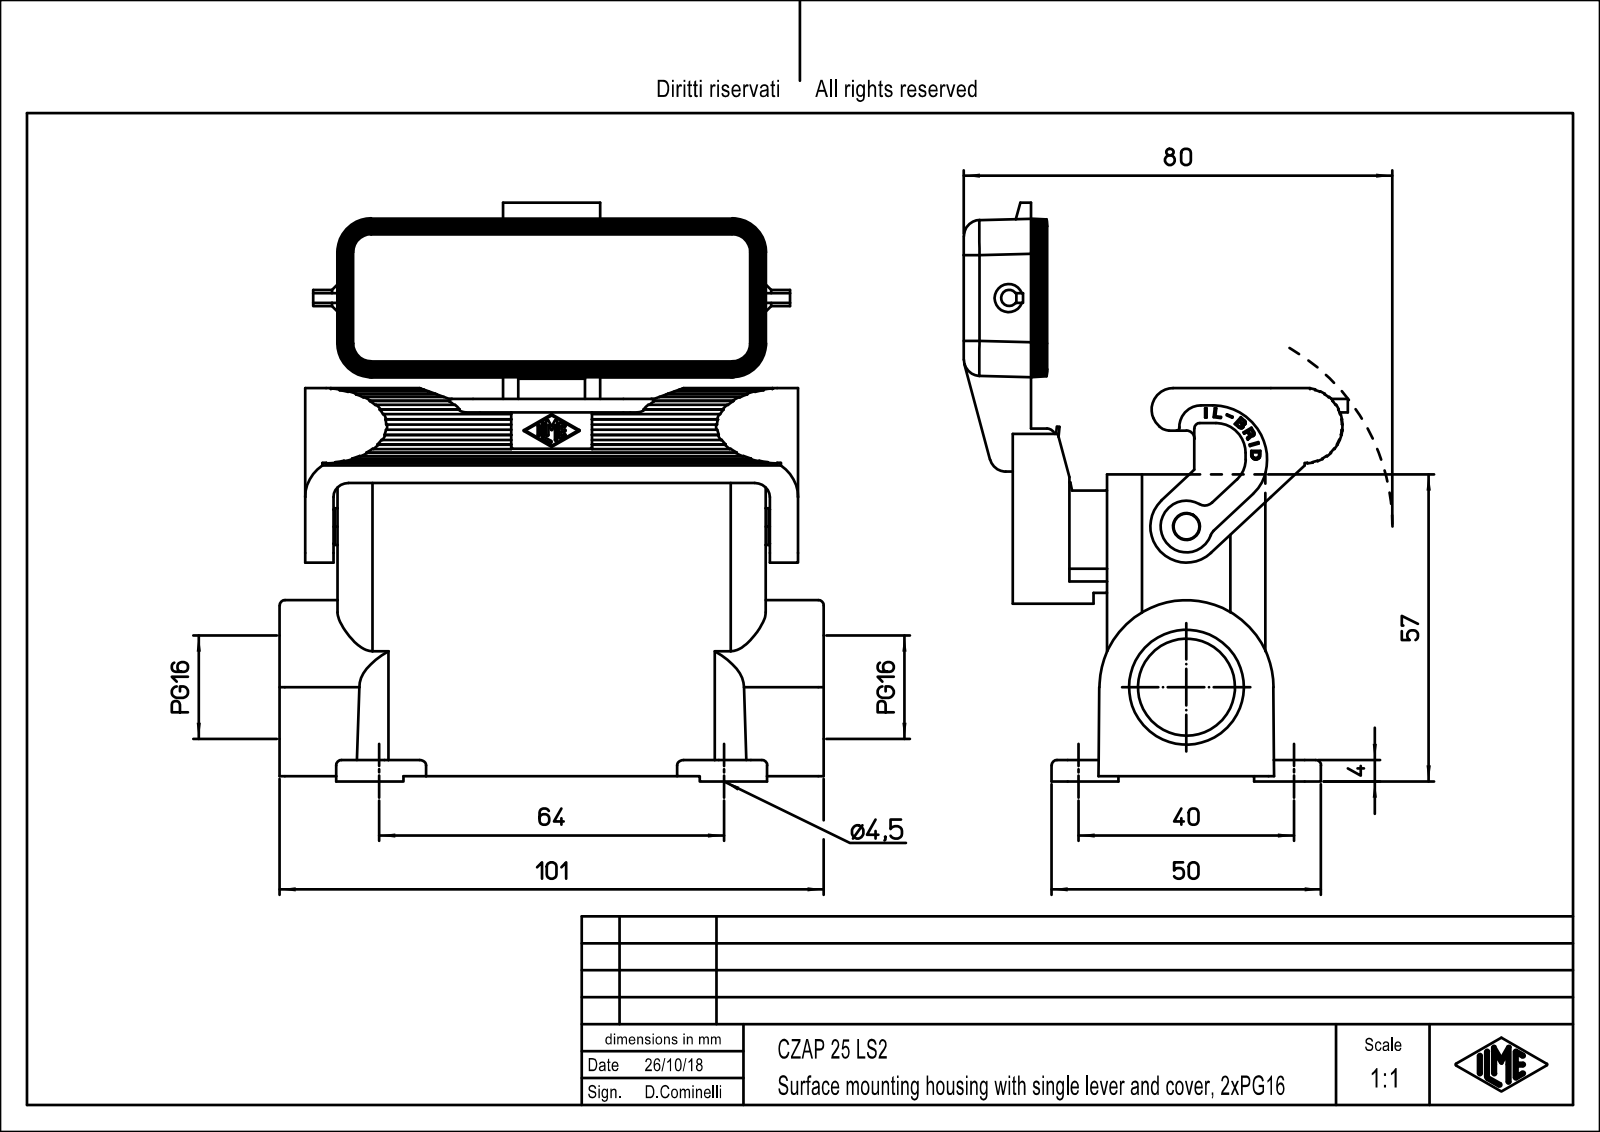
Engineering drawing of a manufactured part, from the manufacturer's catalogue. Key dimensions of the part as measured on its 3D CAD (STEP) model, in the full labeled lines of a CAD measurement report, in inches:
Part name (STEP PRODUCT): CZAP_25_LS2
STEP written by: PTC Creo Elements/Direct Modeling 19.0E 27-Jun-2016 (C) Parametric Technology GmbH (AUTOMOTIVE_DESIGN)
Units: inches
Bodies: 1 solid, 856 faces (594 planar, 219 cylindrical, 43 other)
Overall size (bounding box): 4.228 × 3.976 × 2.807
Volume: 5.259 in³ · Surface area: 87.16 in²
Round holes (diameter × count): ⌀0.118 ×4, ⌀0.177 ×4, ⌀0.197 ×1, ⌀0.756 ×1, ⌀1.068 ×1
Round bosses / shafts (diameter × count): ⌀0.276 ×1, ⌀0.268 ×1, ⌀0.189 ×1, ⌀0.118 ×1
Partial cylindrical surfaces — rounded edges, fillets, slot ends (radius × count): R0.039 ×17, R0.008 ×15, R0.118 ×12, R0.138 ×12, R0.256 ×8, R0.02 ×7, R0.126 ×4, R0.236 ×4
Main face-to-face distances: 0.109, 1.049, 1.157, 0.94, 2.205, 0.079, 0.118, 2.126, 2.017, 1.077
Hole centre spacings: 0.474, 1.103, 2.602, 2.786, 0.63, 1.575, 2.52, 2.598
